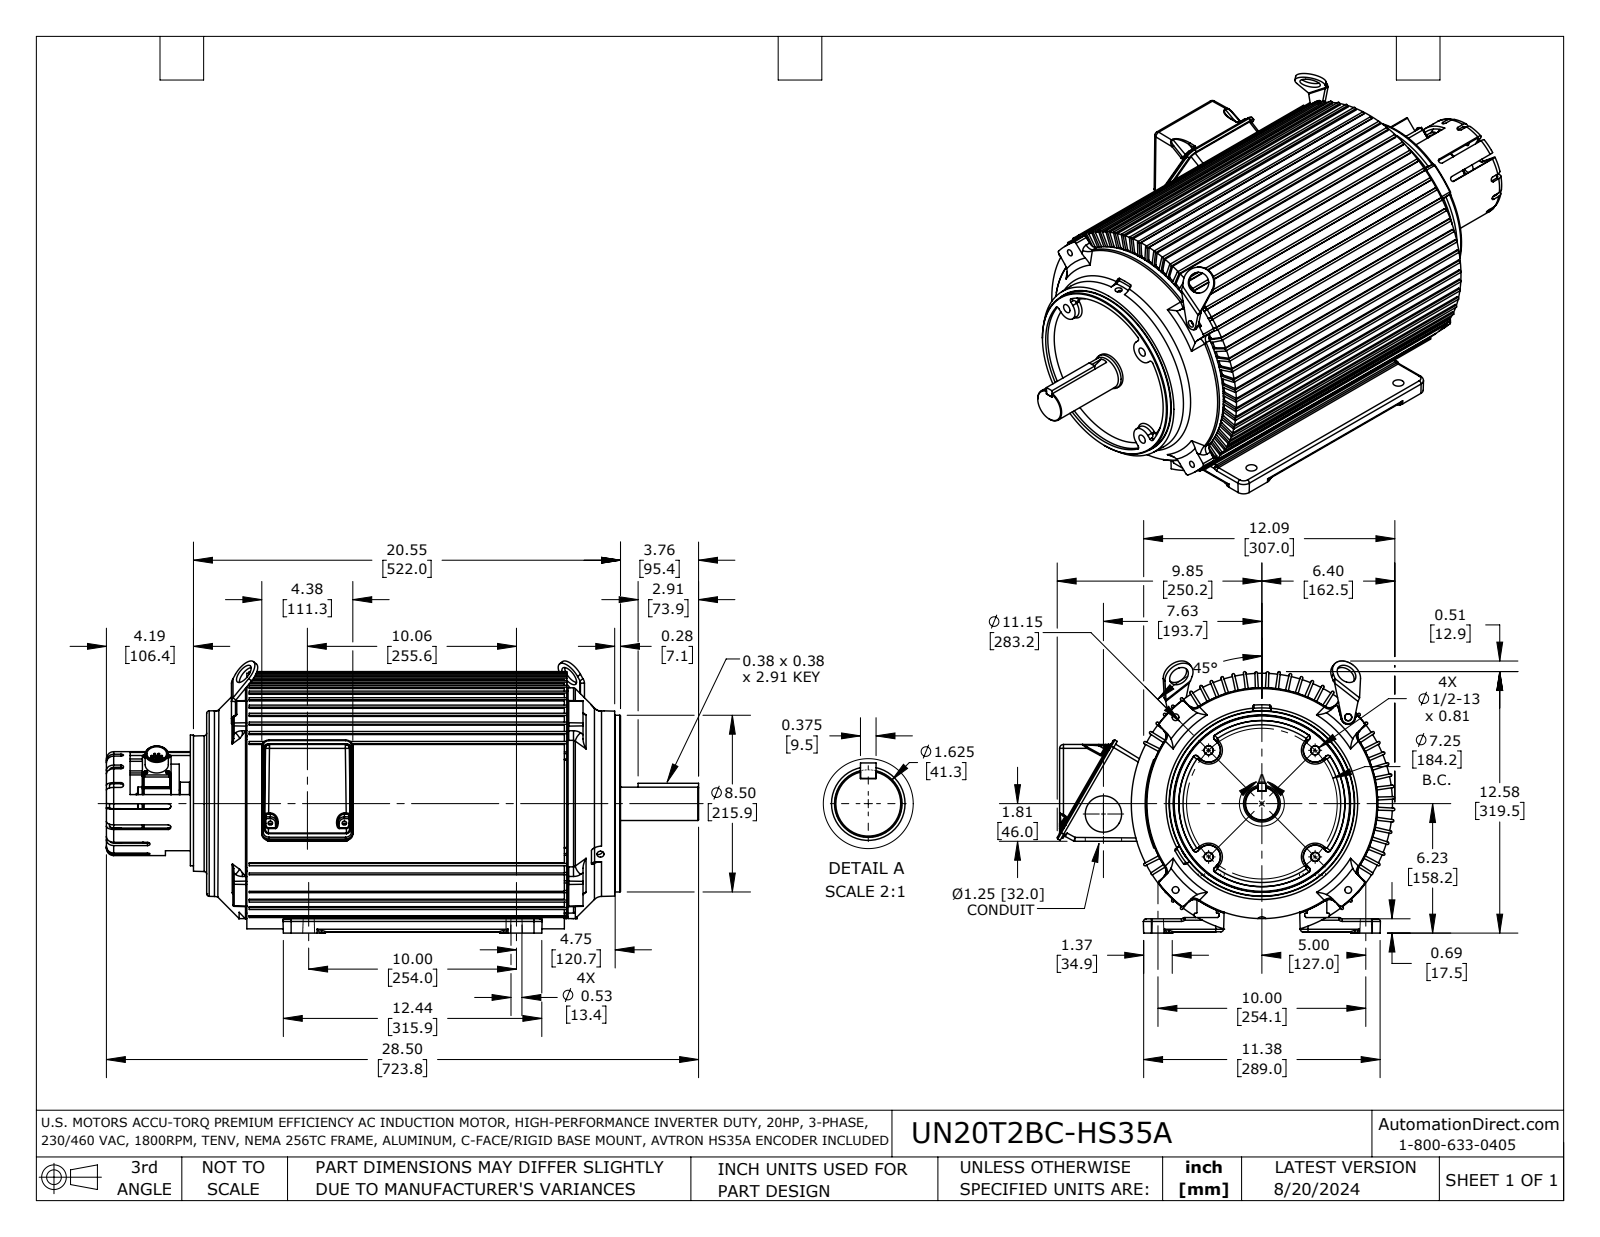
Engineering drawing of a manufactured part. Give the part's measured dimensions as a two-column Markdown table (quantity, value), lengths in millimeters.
| quantity | value |
| --- | --- |
| part name | UN20T2BC-HS35A |
| STEP written by | SolidWorks 2021 (AUTOMOTIVE_DESIGN) |
| units | millimeters |
| bodies | 20 solids, 2725 faces (811 planar, 911 cylindrical, 1003 other) |
| overall size | 723.8 × 412.7 × 332.8 |
| volume | 38 310 000 mm³ |
| surface area | 1 244 000 mm² |
| round holes (diameter × count) | 10.2 × 6, 3 × 4, 5.1 × 4, 8 × 4, 8.3 × 4, 8.7 × 4, 3.5 × 3, 25.4 × 3, 2.7 × 2, 44.5 × 2, 12.7 × 1, 24 × 1 |
| round bosses / shafts (diameter × count) | 1.8 × 8, 4.4 × 4, 3 × 4, 3.8 × 3, 1.8 × 2, 319.3 × 1, 215.9 × 1, 127 × 1 |
| partial cylindrical surfaces (radius × count) | 1.6 × 209, 3.2 × 72, 1.5 × 62, 0.8 × 38, 4.8 × 24, 5.6 × 12, 4.6 × 8, 0.4 × 6 |
| main face-to-face distances | 15.9, 3.2, 8, 539.9, 43.6, 496.3, 27.4, 16.1, 512.4, 34.9 |
| hole center spacings | 53.4, 74.6, 110.6, 121.9, 166.9, 183.4, 52.7, 56.7 |
